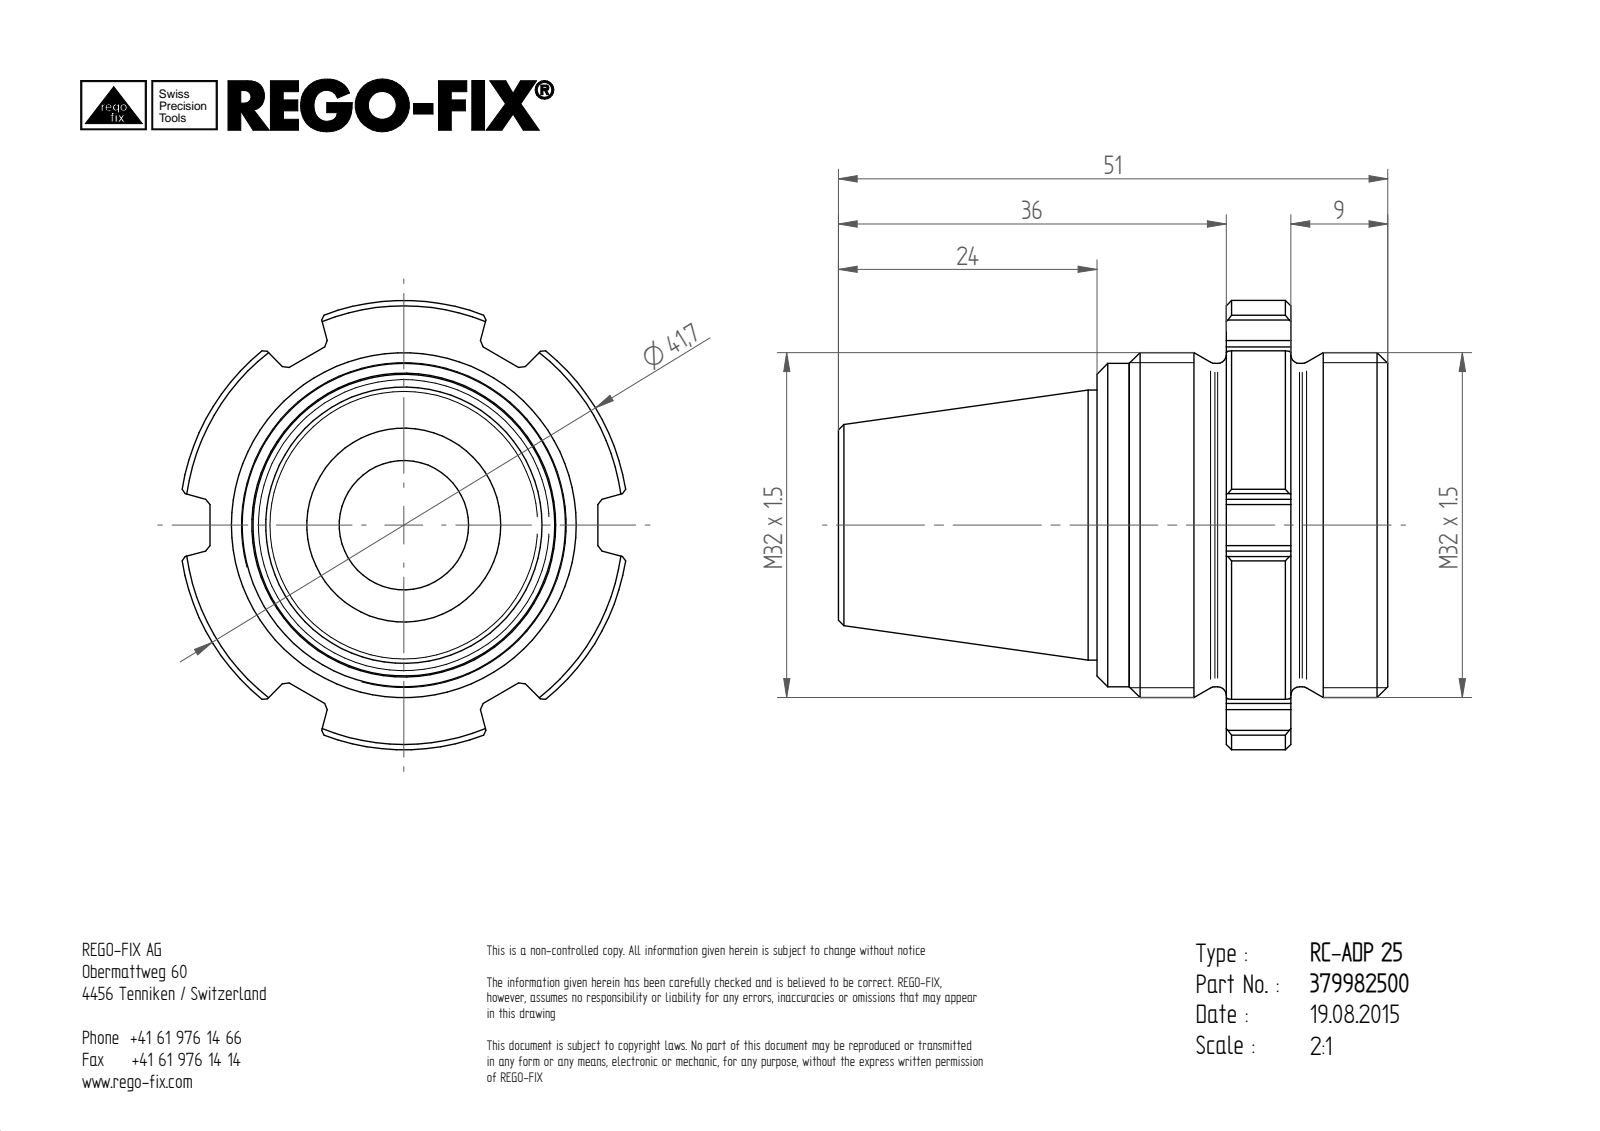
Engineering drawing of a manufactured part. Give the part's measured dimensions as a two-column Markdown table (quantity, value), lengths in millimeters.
| quantity | value |
| --- | --- |
| part name | 0004315; 0004051-oa0; 0004278-oa1; 0004052-oa2 (+7 more) |
| STEP written by | Unknown (AUTOMOTIVE_DESIGN) |
| units | millimeters |
| bodies | 10 solids, 453 faces (166 planar, 105 cylindrical, 182 other) |
| overall size | 69.91 × 56.5 × 50 |
| volume | 57 639 mm³ |
| surface area | 47 628 mm² |
| round holes (diameter × count) | 4 × 9, 2 × 1, 8 × 1, 8.57 × 1, 12 × 1, 18 × 1, 19 × 1, 21 × 1, 23.5 × 1, 28 × 1, 30.38 × 1, 32.5 × 1 |
| round bosses / shafts (diameter × count) | 50 × 1, 48 × 1, 40.74 × 1, 40.24 × 1, 39.67 × 1, 34.9 × 1, 32 × 1, 30 × 1 |
| partial cylindrical surfaces (radius × count) | 1.5 × 2, 8 × 2, 12.16 × 2, 12.4 × 2, 11.3 × 1, 14.3 × 1, 14.75 × 1, 18 × 1 |
| main face-to-face distances | 0.8, 2, 19, 1.65, 3.65, 17.35, 15.35, 21, 6, 17 |
| hole center spacings | 20 |
